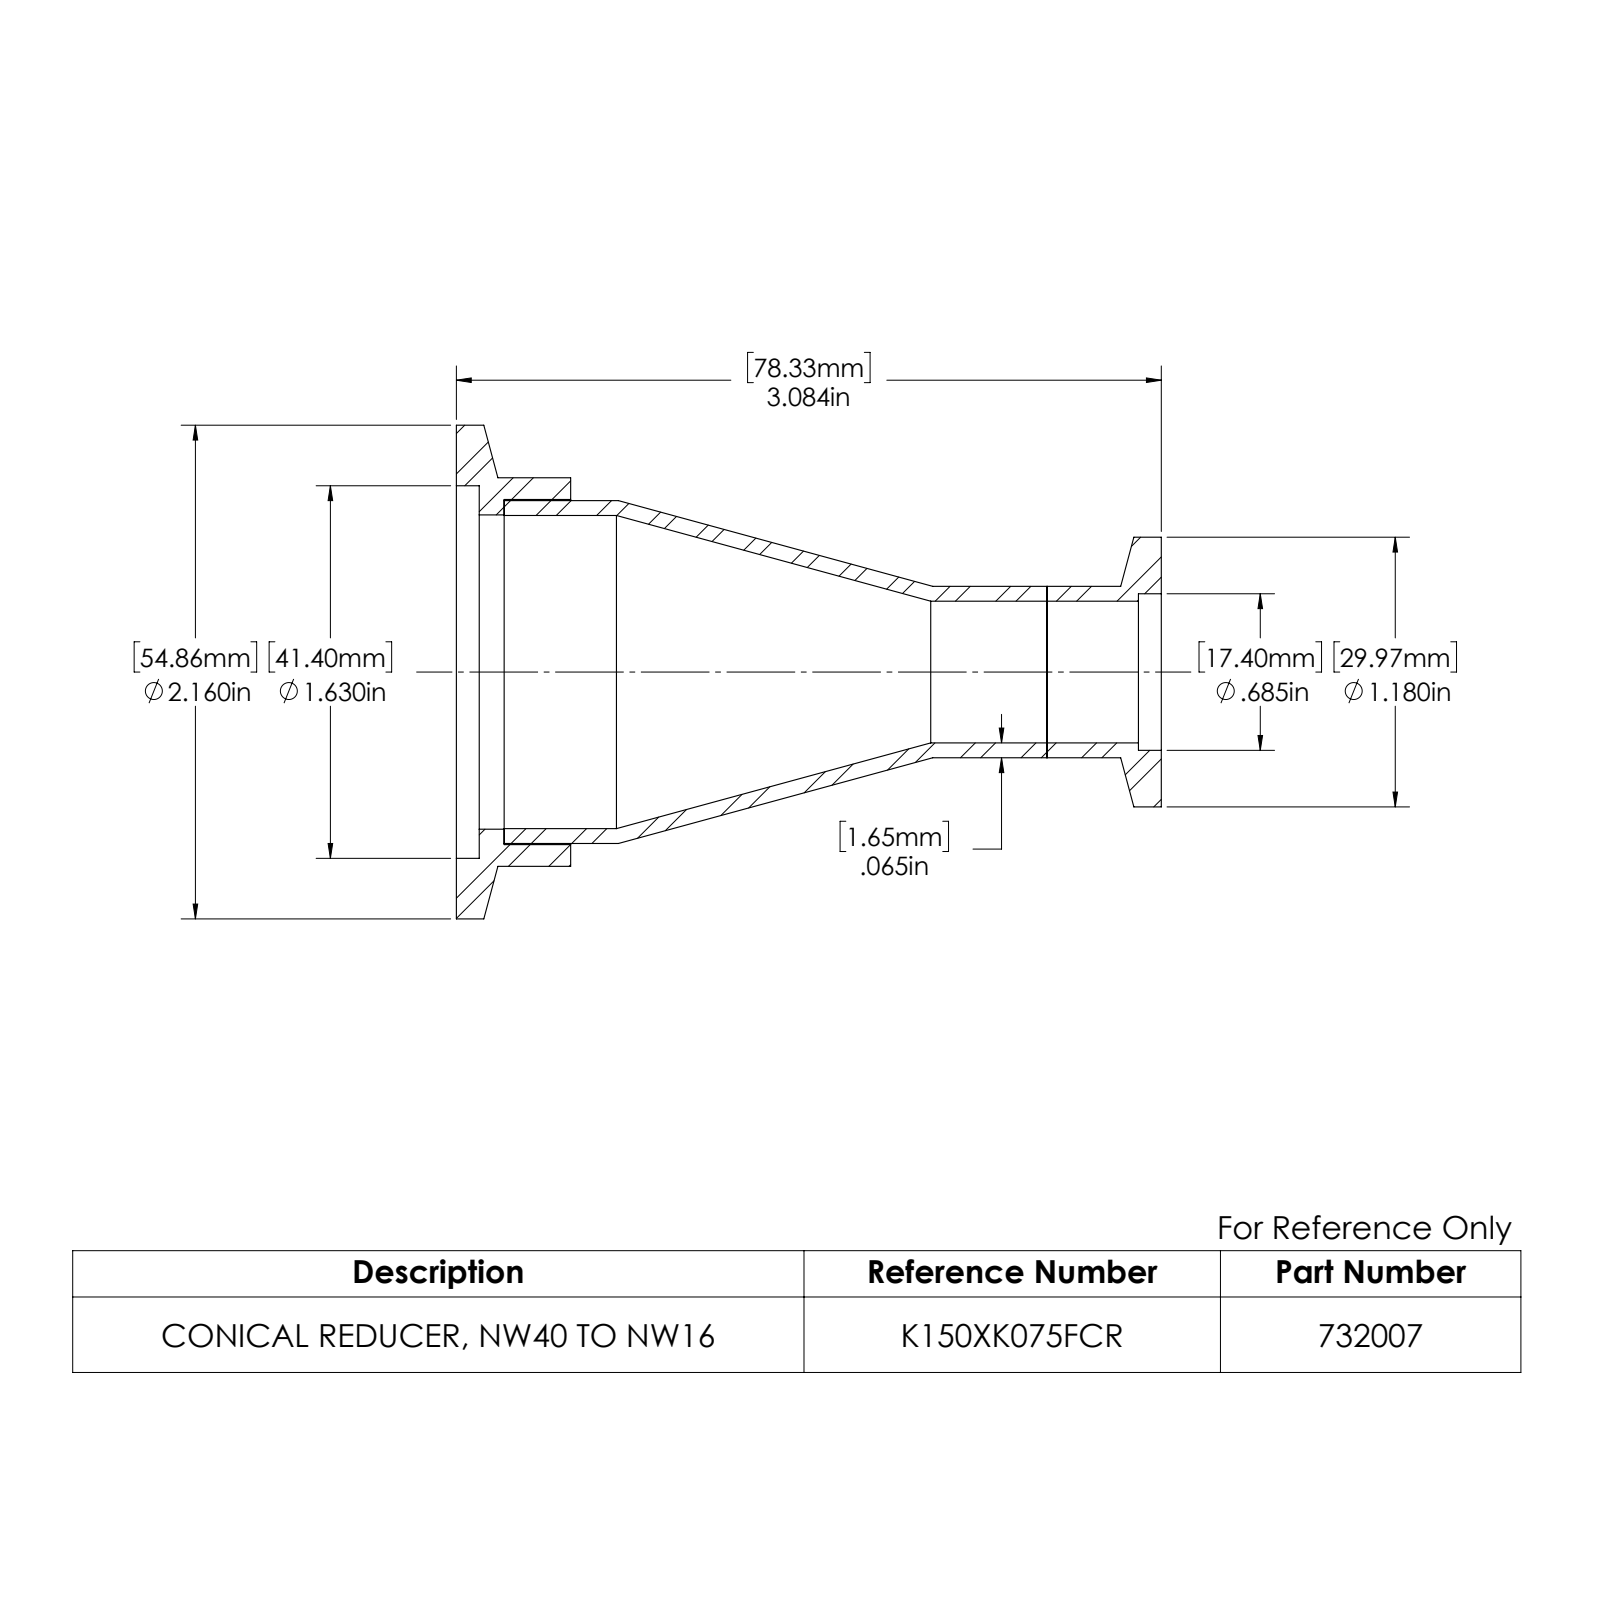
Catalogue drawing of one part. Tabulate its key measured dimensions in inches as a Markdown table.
| quantity | value |
| --- | --- |
| part name | 732007; 713003; 715101 |
| STEP written by | SolidWorks 2022 (AUTOMOTIVE_DESIGN) |
| units | inches |
| bodies | 3 solids, 43 faces (9 planar, 26 cylindrical, 8 other) |
| overall size | 3.084 × 2.16 × 2.16 |
| volume | 1.135 in³ |
| surface area | 29.66 in² |
| round holes (diameter × count) | 0.62 × 1, 0.685 × 1, 1.37 × 1, 1.375 × 1, 1.51 × 1, 1.63 × 1 |
| round bosses / shafts (diameter × count) | 2.16 × 1, 1.7 × 1, 1.5 × 1, 1.18 × 1, 0.75 × 1 |
| main face-to-face distances | 0.5, 2.584, 3.084, 0.1, 2.984, 0.209, 0.109, 2.875, 0.4, 0.291 |
